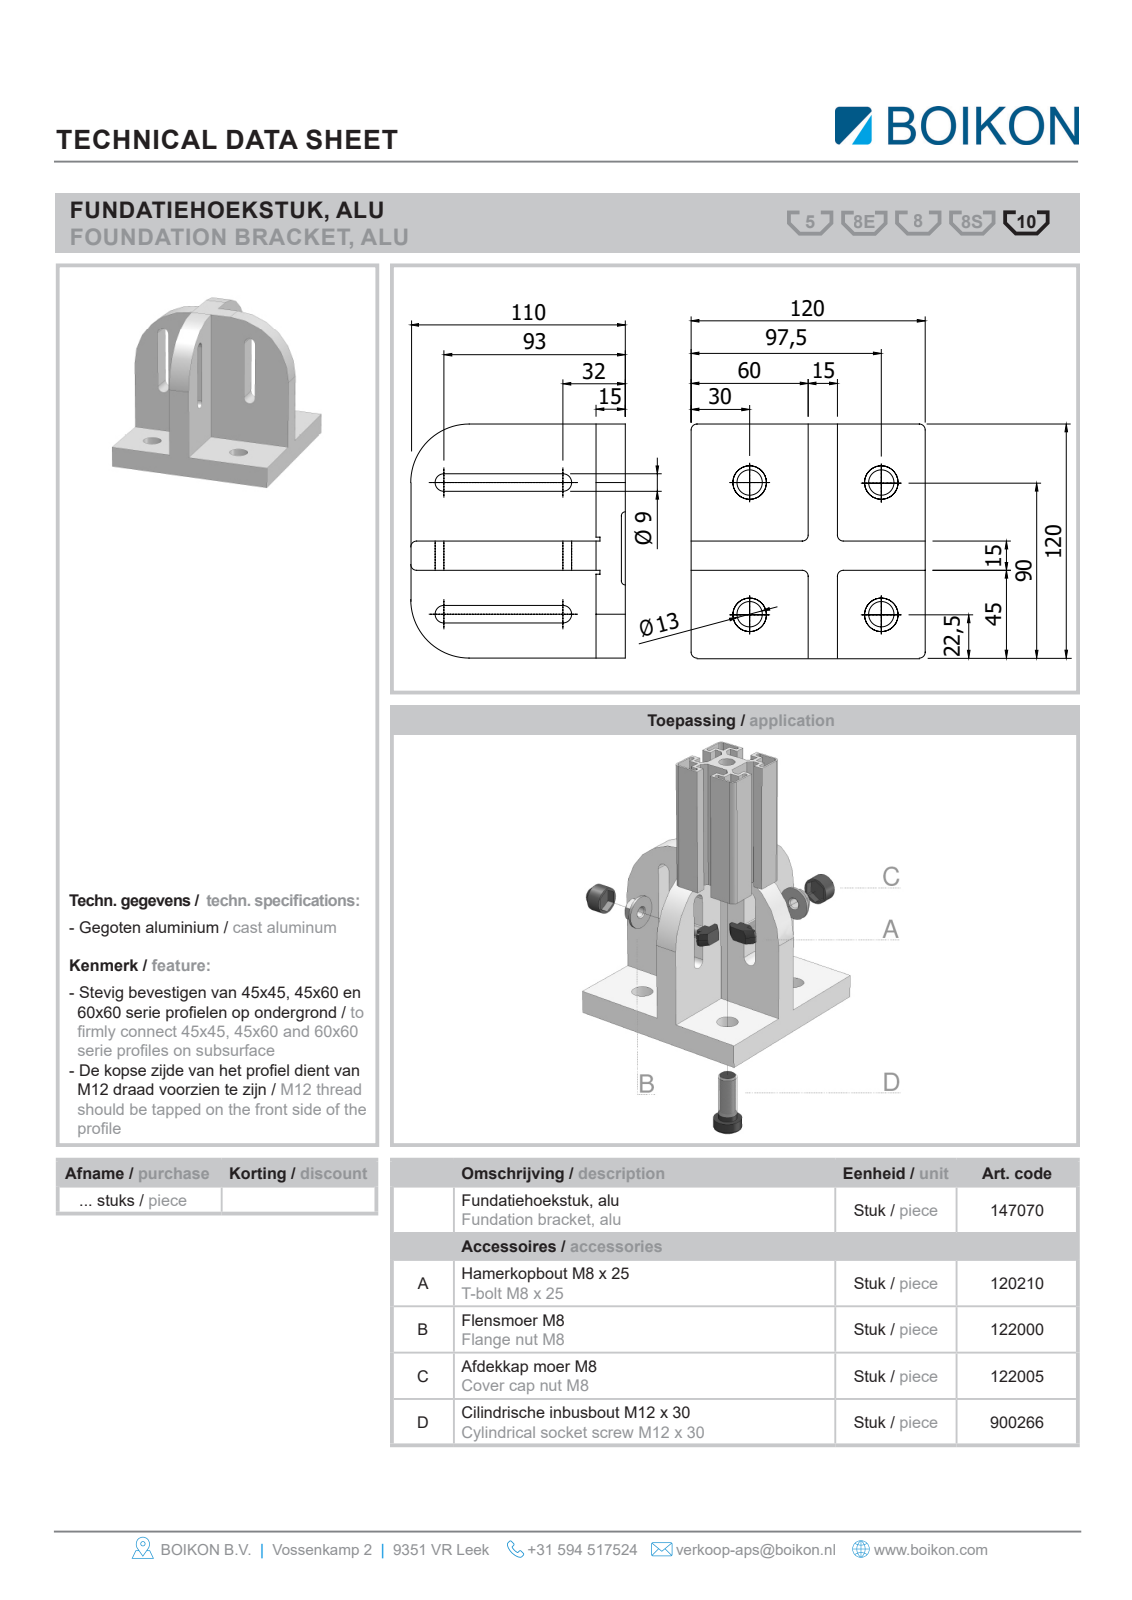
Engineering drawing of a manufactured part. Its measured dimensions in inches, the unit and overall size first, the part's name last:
Units: inches
Overall size (bounding box): 4.724 × 4.724 × 4.331
Round holes (diameter × count): ⌀0.531 ×4, ⌀0.787 ×4
Partial cylindrical surfaces — rounded edges, fillets, slot ends (radius × count): R0.167 ×8, R1.772 ×4
Main face-to-face distances: 0.591, 2.362, 1.772, 4.724, 2.953, 0.719, 1.053, 0.335, 2.657, 1.014
Hole centre spacings: 2.657, 3.758
Volume: 28.8 in³ · Surface area: 127.6 in²
Bodies: 1 solid, 50 faces (30 planar, 20 cylindrical, 0 other)
Part name (STEP PRODUCT): Root; 147070 (geen vooraad)Fundatiehoekstuk aluBOIKON0
STEP written by: HiCAD 2013 1802.4 Build 509 (AUTOMOTIVE_DESIGN)
